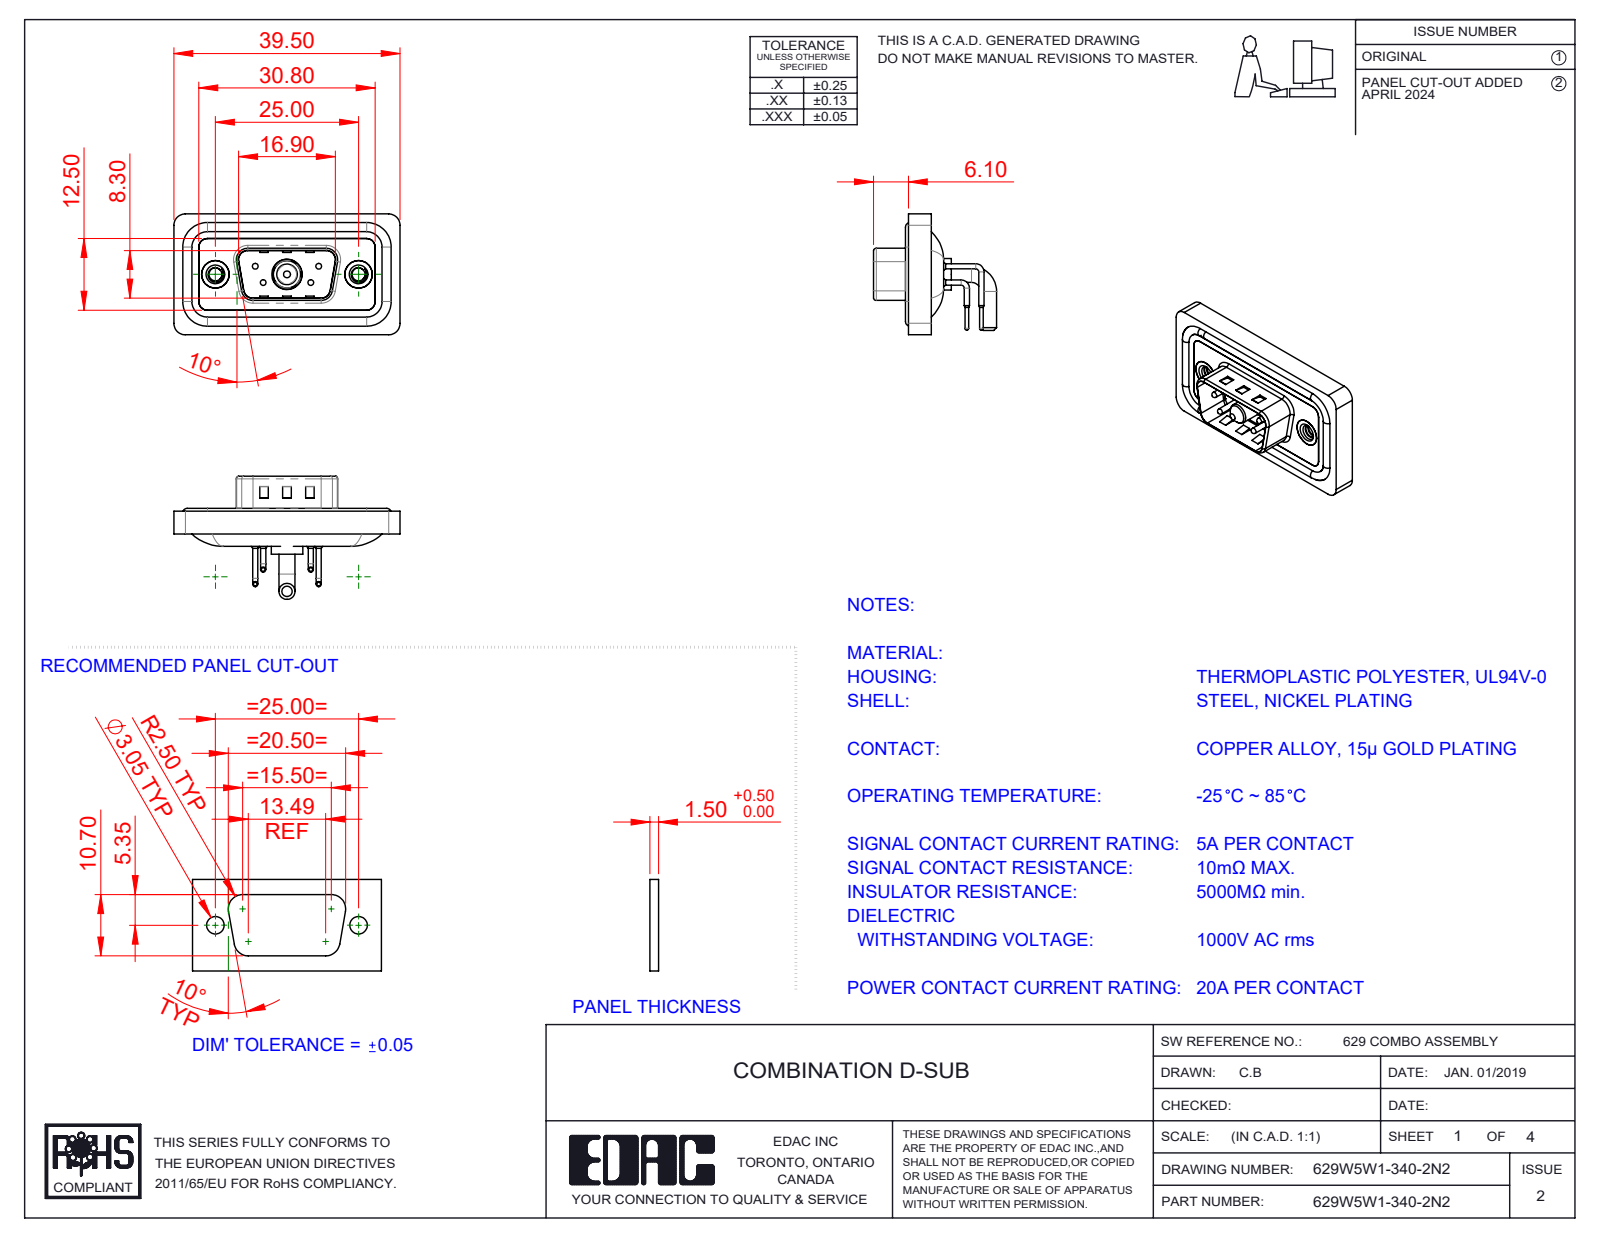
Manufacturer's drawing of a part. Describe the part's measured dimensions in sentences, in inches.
The part is named "629Combo Contact Row 1; 629Combo Waterproof Housing_09 Contacts; 629Combo Shell Rear_09 Contacts; 629Combo Contact Row 2 (+5 more)". Its 3-D file was written by "SolidWorks 2023 (CONFIG_CONTROL_DESIGN)". It is 13 solids with 894 faces: 411 planar, 345 cylindrical and 138 other. Overall it measures 1.555 by 0.846 by 0.831 inches. Its volume is 0.274 cubic inches and its surface area 11.1 square inches. Round holes: 4 of diameter 0.03, 4 of diameter 0.063, 4 of diameter 0.079, 2 of diameter 0.089, 2 of diameter 0.157, 2 of diameter 0.189, 2 of diameter 0.197, 1 of diameter 0.191, 1 of diameter 0.209. Round bosses or shafts: 8 of diameter 0.035, 4 of diameter 0.063, 4 of diameter 0.059, 4 of diameter 0.039, 4 of diameter 0.026, 2 of diameter 0.193, 2 of diameter 0.11, 1 of diameter 0.217. Partial cylindrical surfaces (rounded edges, fillets, slot ends): 18 of radius 0.059, 18 of radius 0.079, 8 of radius 0.02, 8 of radius 0.063, 4 of radius 0.01, 4 of radius 0.024, 4 of radius 0.026, 4 of radius 0.035. The main face-to-face distances are 0.016, 0.114, 0.043, 0.031, 0.083, 0.098, 0.063, 0.122, 0.177, 0.059. The hole center spacings are 0.124, 0.225, 0.28, 0.492, 0.713, 0.173, 0.173, 0.327.
